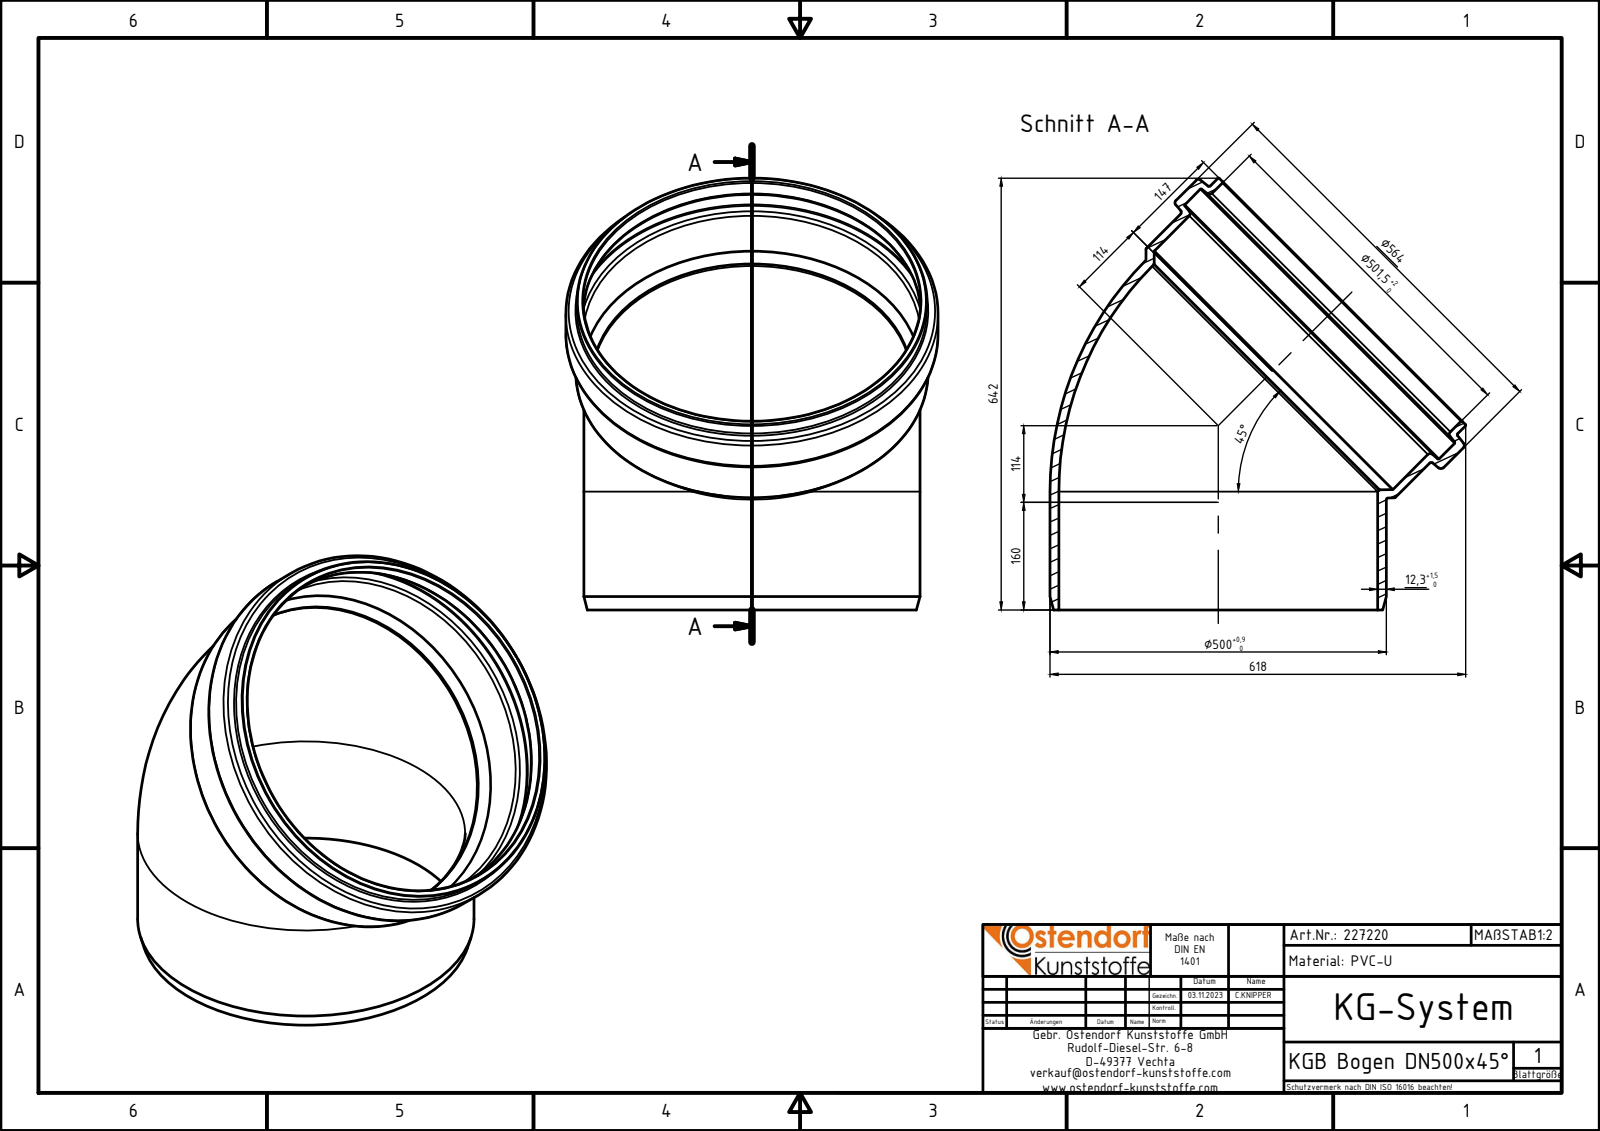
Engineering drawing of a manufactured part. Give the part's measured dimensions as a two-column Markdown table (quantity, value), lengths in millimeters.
| quantity | value |
| --- | --- |
| part name | 227220z |
| STEP written by | Autodesk Inventor 2024 (AUTOMOTIVE_DESIGN) |
| units | millimeters |
| bodies | 1 solid, 35 faces (2 planar, 9 cylindrical, 24 other) |
| overall size | 642 × 618 × 553.6 |
| volume | 10 290 000 mm³ |
| surface area | 1 764 000 mm² |
| round holes (diameter × count) | 474 × 2, 501.5 × 2, 534.6 × 1 |
| round bosses / shafts (diameter × count) | 553.6 × 1, 523.7 × 1, 520.5 × 1, 500 × 1 |
